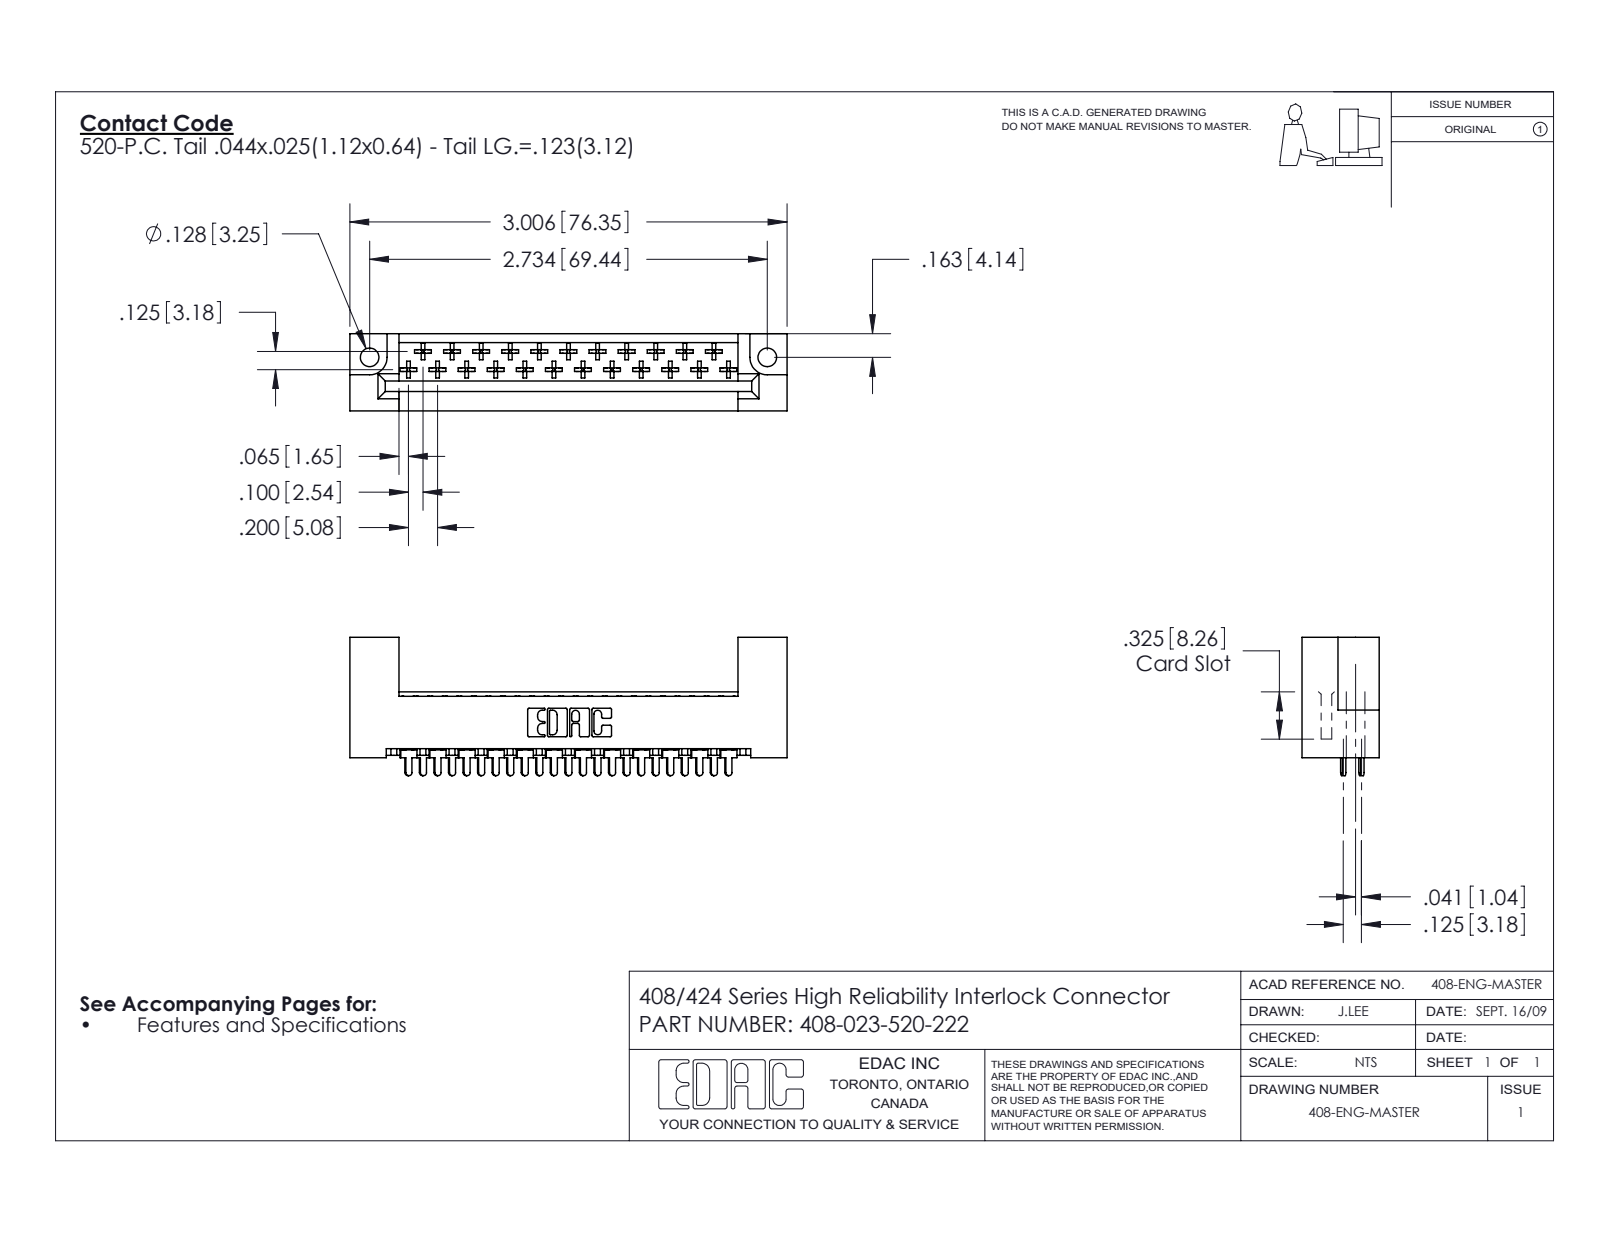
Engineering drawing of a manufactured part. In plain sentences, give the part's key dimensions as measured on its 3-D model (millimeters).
The part is named "408-290-001_408-290-120; 408 Part_023 - 2; 408-023-520-222". Its 3-D file was written by "SolidWorks 2016 (CONFIG_CONTROL_DESIGN)". It is 24 solids with 1404 faces: 1055 planar, 257 cylindrical and 92 other. Overall it measures 76.4 by 24.2 by 13.5 millimeters. Its volume is 9 930 cubic millimeters and its surface area 10 900 square millimeters. Round holes: 2 of diameter 3.3. Partial cylindrical surfaces (rounded edges, fillets, slot ends): 138 of radius 0.3, 25 of radius 0.5, 23 of radius 0.6, 22 of radius 0.3, 6 of radius 0.2, 6 of radius 0.8, 3 of radius 0.7, 2 of radius 3. The main face-to-face distances are 13.5, 3.2, 2.5, 0.6, 0.6, 9.2, 10.1, 6, 6.6, 8.3. The hole center spacings are 69.4.
